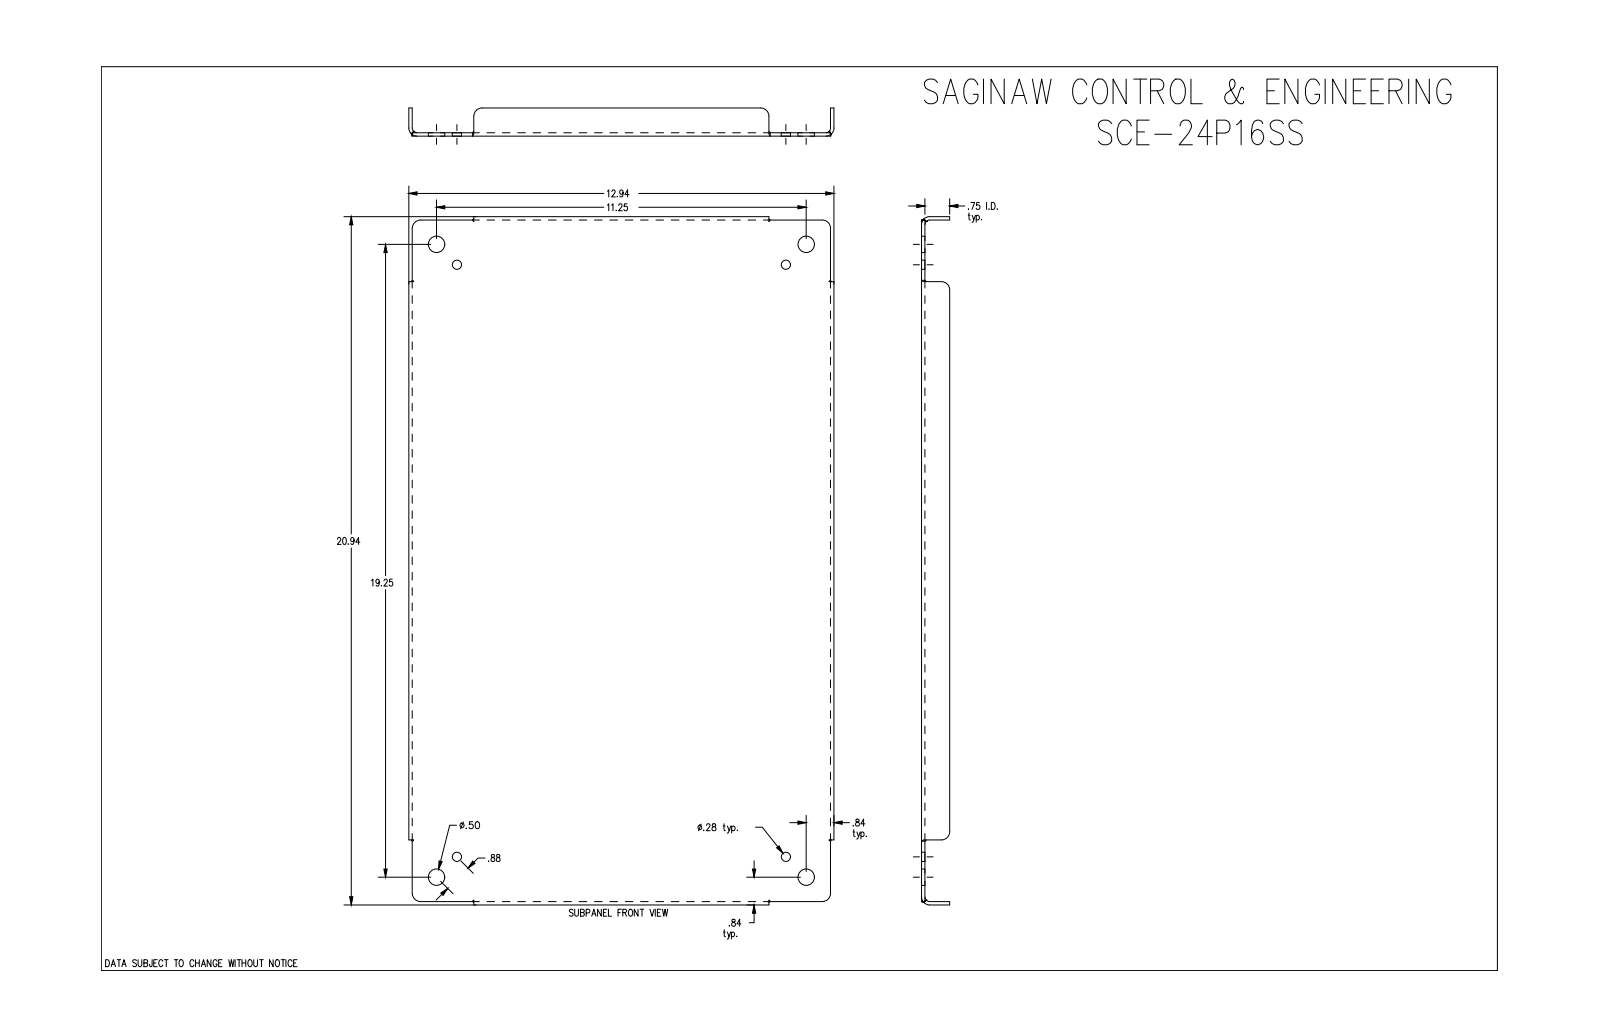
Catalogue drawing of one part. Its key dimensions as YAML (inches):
part_name: "SCE-24P16SS"
step_written_by: "SolidWorks 2019 (CONFIG_CONTROL_DESIGN)"
units: inches
bodies: {solids: 1, faces: 82, planar: 30, cylindrical: 28, other: 24}
overall_size: [20.941, 12.941, 0.858]
volume: 31.52
surface_area: 614.6
round_holes:
  - {diameter: 0.281, count: 4}
  - {diameter: 0.5, count: 4}
partial_cylinders:
  - {radius: 0.25, count: 8}
  - {radius: 0.246, count: 4}
  - {radius: 0.142, count: 2}
  - {radius: 0.143, count: 2}
face_to_face_distances: [0.104, 12.838, 20.838, 12.734, 12.942, 20.734, 20.942, 0.754, 0.858, 1.979]
hole_center_spacings: [0.875, 10.651, 18.643, 21.454, 10.014, 11.252, 18.014, 19.252]
